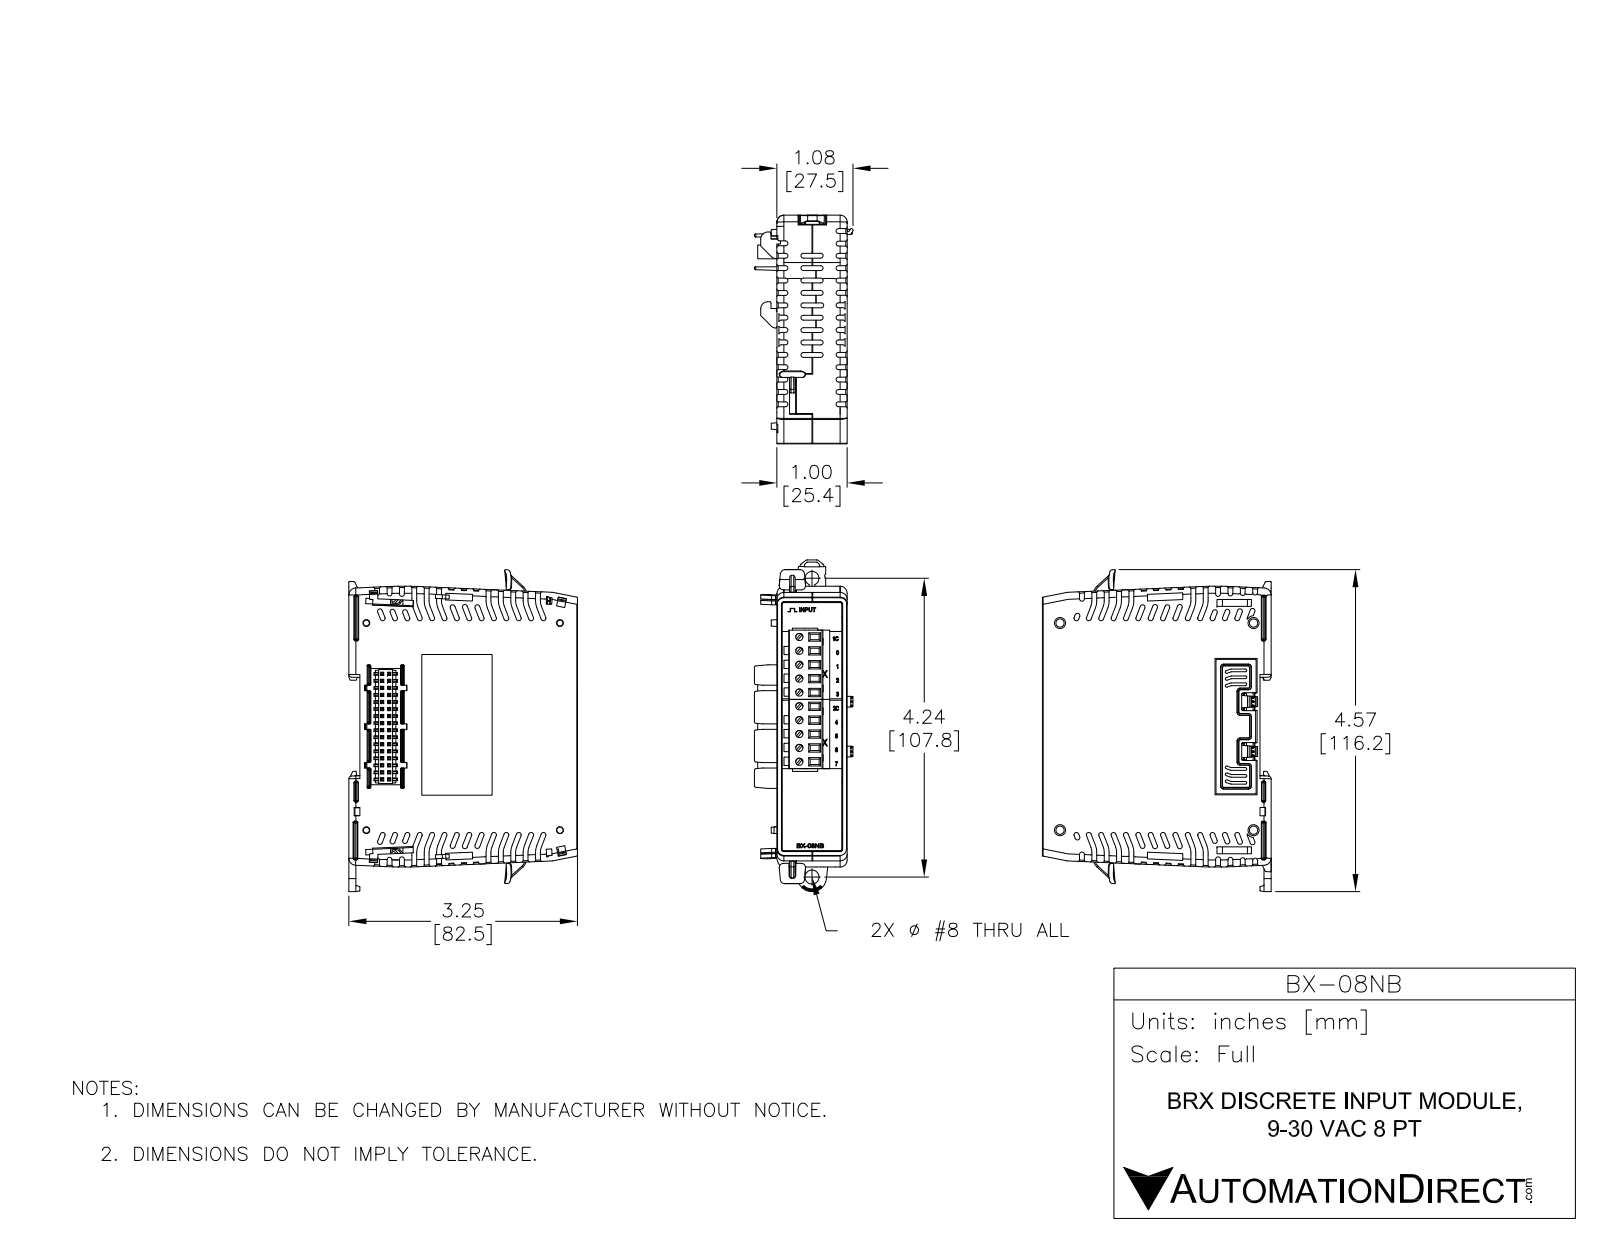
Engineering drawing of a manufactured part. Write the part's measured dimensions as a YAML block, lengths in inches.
part_name: "BX-08NB"
step_written_by: "SolidWorks 2017 (AUTOMOTIVE_DESIGN)"
units: inches
bodies: {solids: 22, faces: 3576, planar: 2545, cylindrical: 563, other: 468}
overall_size: [4.586, 3.311, 1.402]
volume: 11.59
surface_area: 72.76
round_holes:
  - {diameter: 0.047, count: 2}
  - {diameter: 0.065, count: 2}
  - {diameter: 0.118, count: 2}
  - {diameter: 0.118, count: 2}
  - {diameter: 0.199, count: 1}
round_bosses_or_shafts:
  - {diameter: 0.062, count: 2}
  - {diameter: 0.059, count: 2}
partial_cylinders:
  - {radius: 0.005, count: 102}
  - {radius: 0.01, count: 47}
  - {radius: 0.02, count: 34}
  - {radius: 0.005, count: 24}
  - {radius: 0.008, count: 21}
  - {radius: 0.117, count: 14}
  - {radius: 0.039, count: 13}
  - {radius: 0.01, count: 12}
face_to_face_distances: [1, 3.211, 3.22, 0.475, 0.1, 0.157, 3.053, 3.063, 0.787, 0.63]
hole_center_spacings: [0.1, 0.824, 0.919, 1.3, 2.093, 2.193, 2.585, 2.617]
